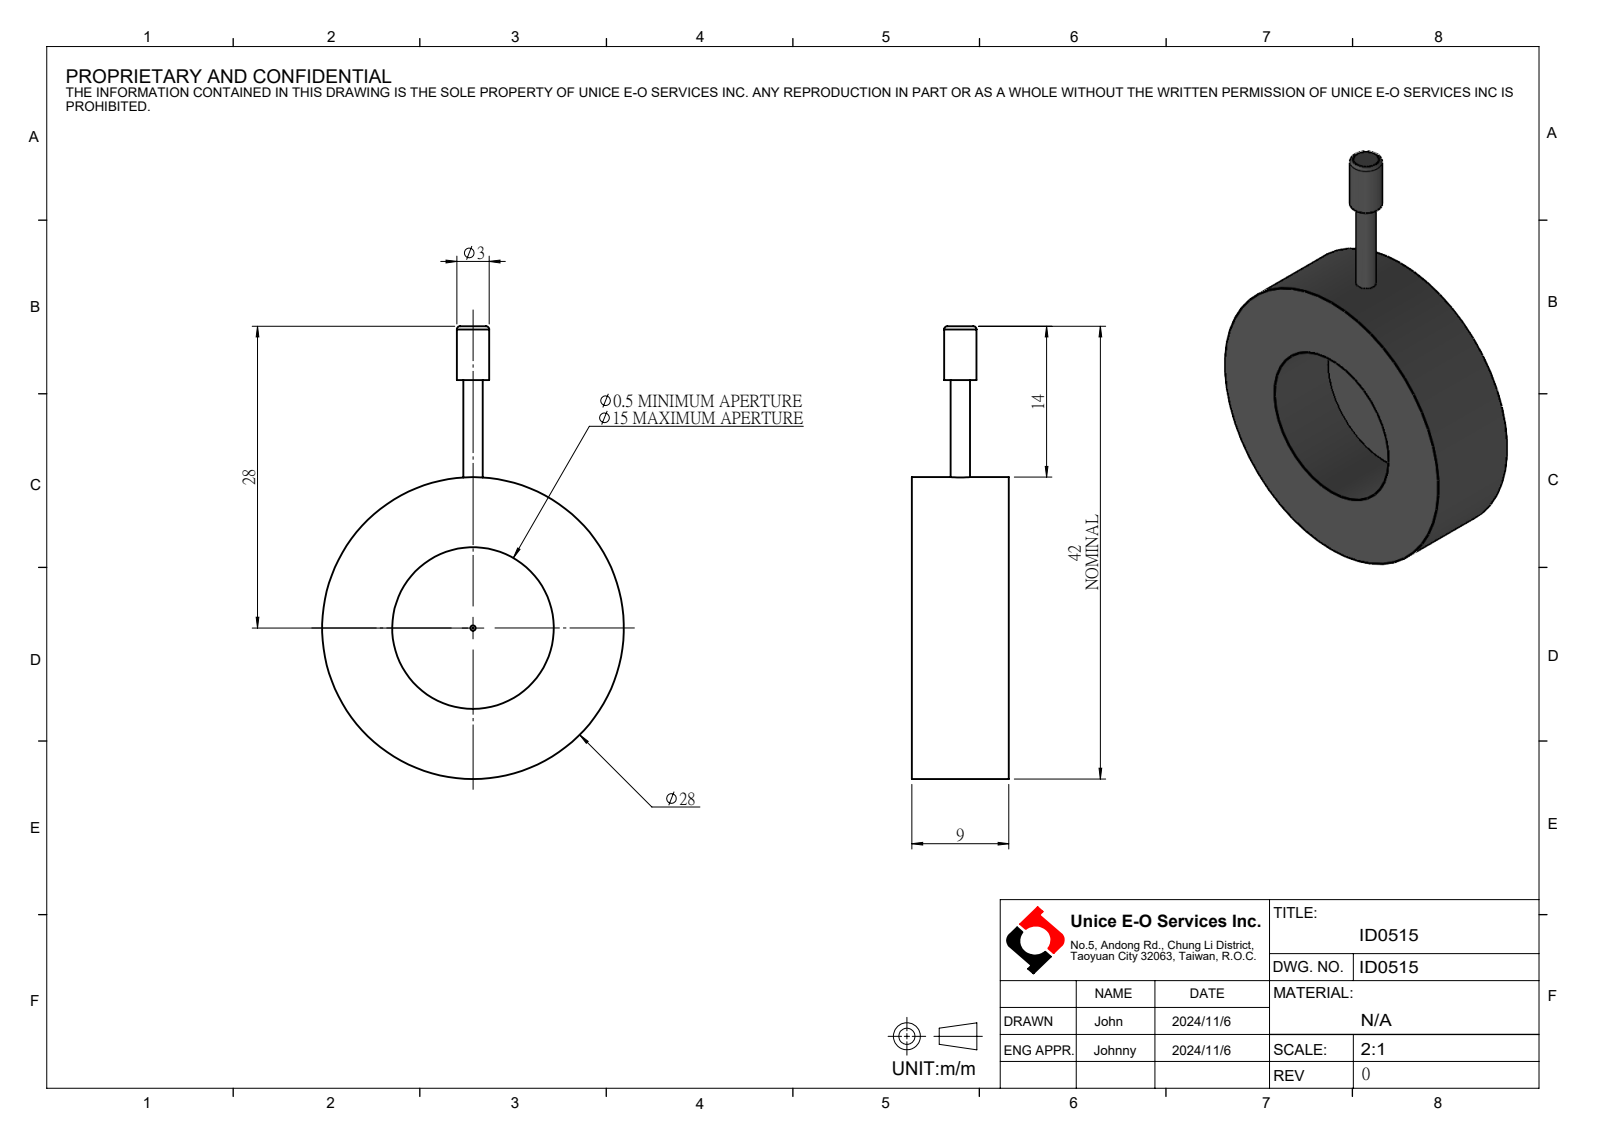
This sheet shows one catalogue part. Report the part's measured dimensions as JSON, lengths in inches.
{"part_name": "ID0515", "step_written_by": "SolidWorks 2022 (CONFIG_CONTROL_DESIGN)", "units": "inches", "bodies": {"solids": 1, "faces": 13, "planar": 6, "cylindrical": 6, "other": 1}, "overall_size": [1.654, 1.102, 0.354], "volume_in3": 0.255, "surface_area_in2": 3.886, "round_holes": [[0.02, 1], [0.591, 1]], "round_bosses_or_shafts": [[1.102, 1], [0.118, 1], [0.071, 1]], "face_to_face_distances": [0.354, 0.039, 0.079, 0.315, 0.276, 0.197]}
